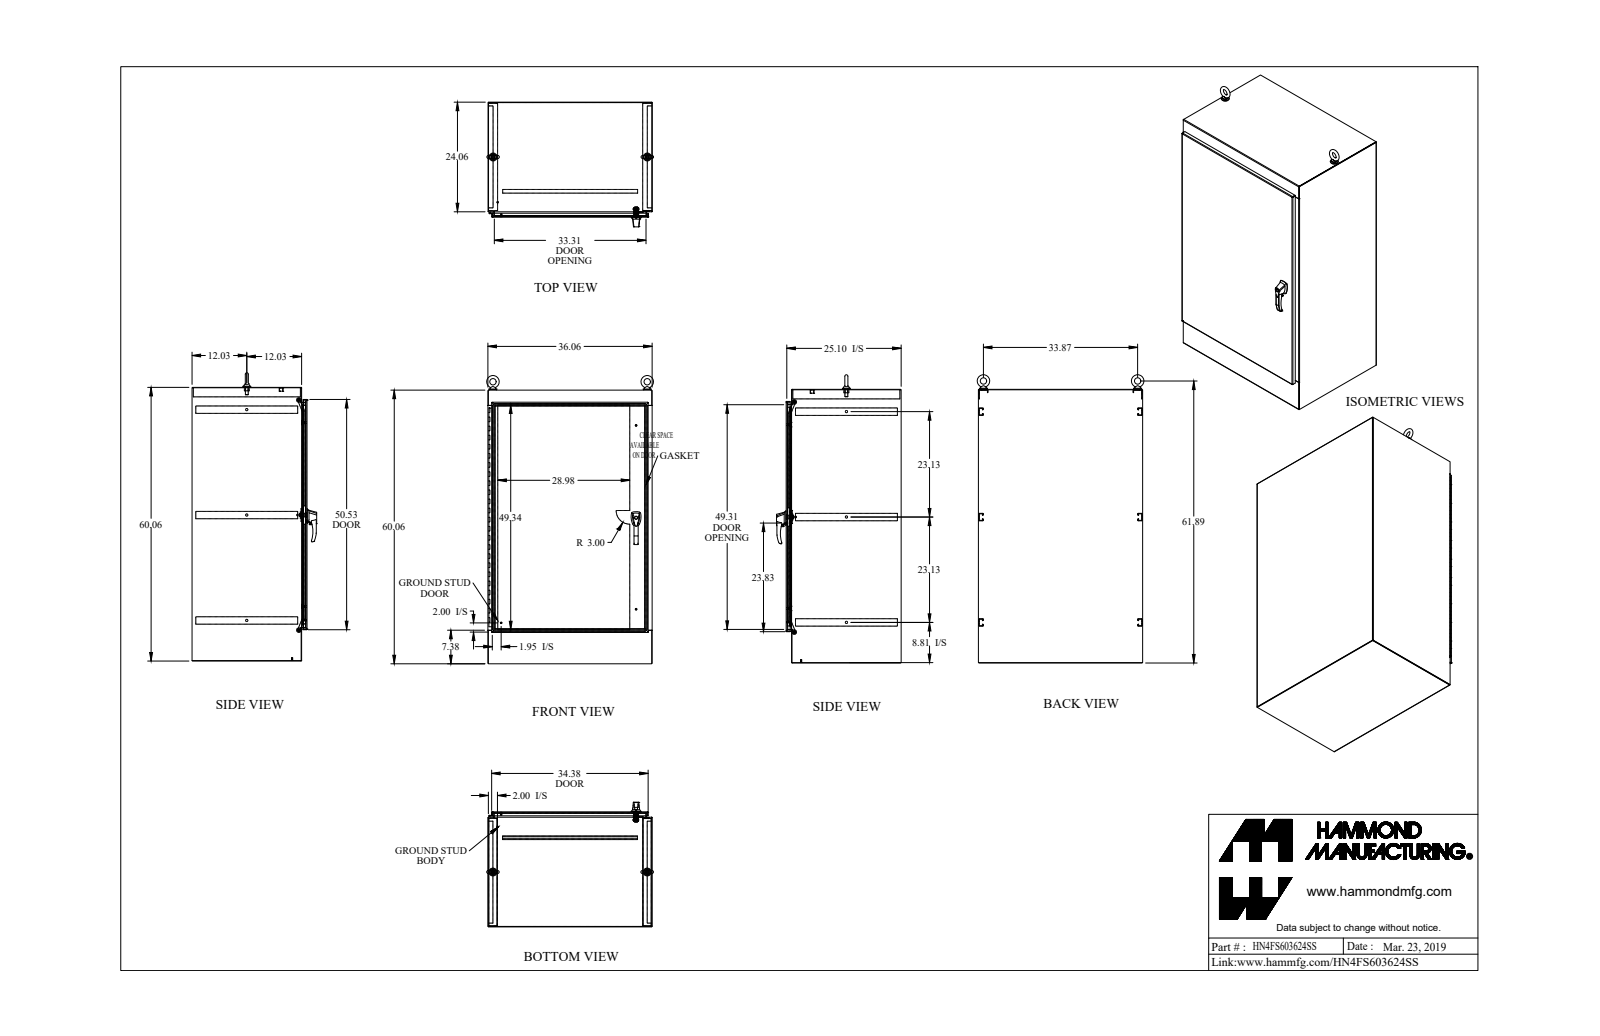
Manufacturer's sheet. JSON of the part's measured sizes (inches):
{"part_name": "HN4FS603624SS", "step_written_by": "SolidWorks 2018 (AUTOMOTIVE_DESIGN)", "units": "inches", "bodies": {"solids": 52, "faces": 1745, "planar": 812, "cylindrical": 768, "other": 165}, "overall_size": [63.256, 36.604, 27.362], "volume_in3": 1033, "surface_area_in2": 21656, "round_holes": [[0.304, 8], [0.35, 7], [0.5, 3], [0.25, 2], [0.257, 2], [0.28, 2], [0.281, 2], [0.313, 2], [0.39, 2], [0.413, 2], [0.527, 2], [0.625, 2]], "round_bosses_or_shafts": [[1.75, 2], [1.5, 2], [1.25, 2], [1, 2], [0.75, 2], [0.738, 2], [0.63, 2], [0.625, 2]], "partial_cylinders_radius": [[0.043, 42], [0.138, 36], [0.5, 23], [0.125, 22], [0.018, 16], [0.048, 15], [0.06, 15], [0.143, 15]], "face_to_face_distances": [0.095, 25.152, 35.965, 25.057, 35.87, 25.247, 59.965, 36.06, 23.965, 1.187], "hole_center_spacings": [6, 12, 18, 24, 30, 1.126, 1.287, 7.5]}
